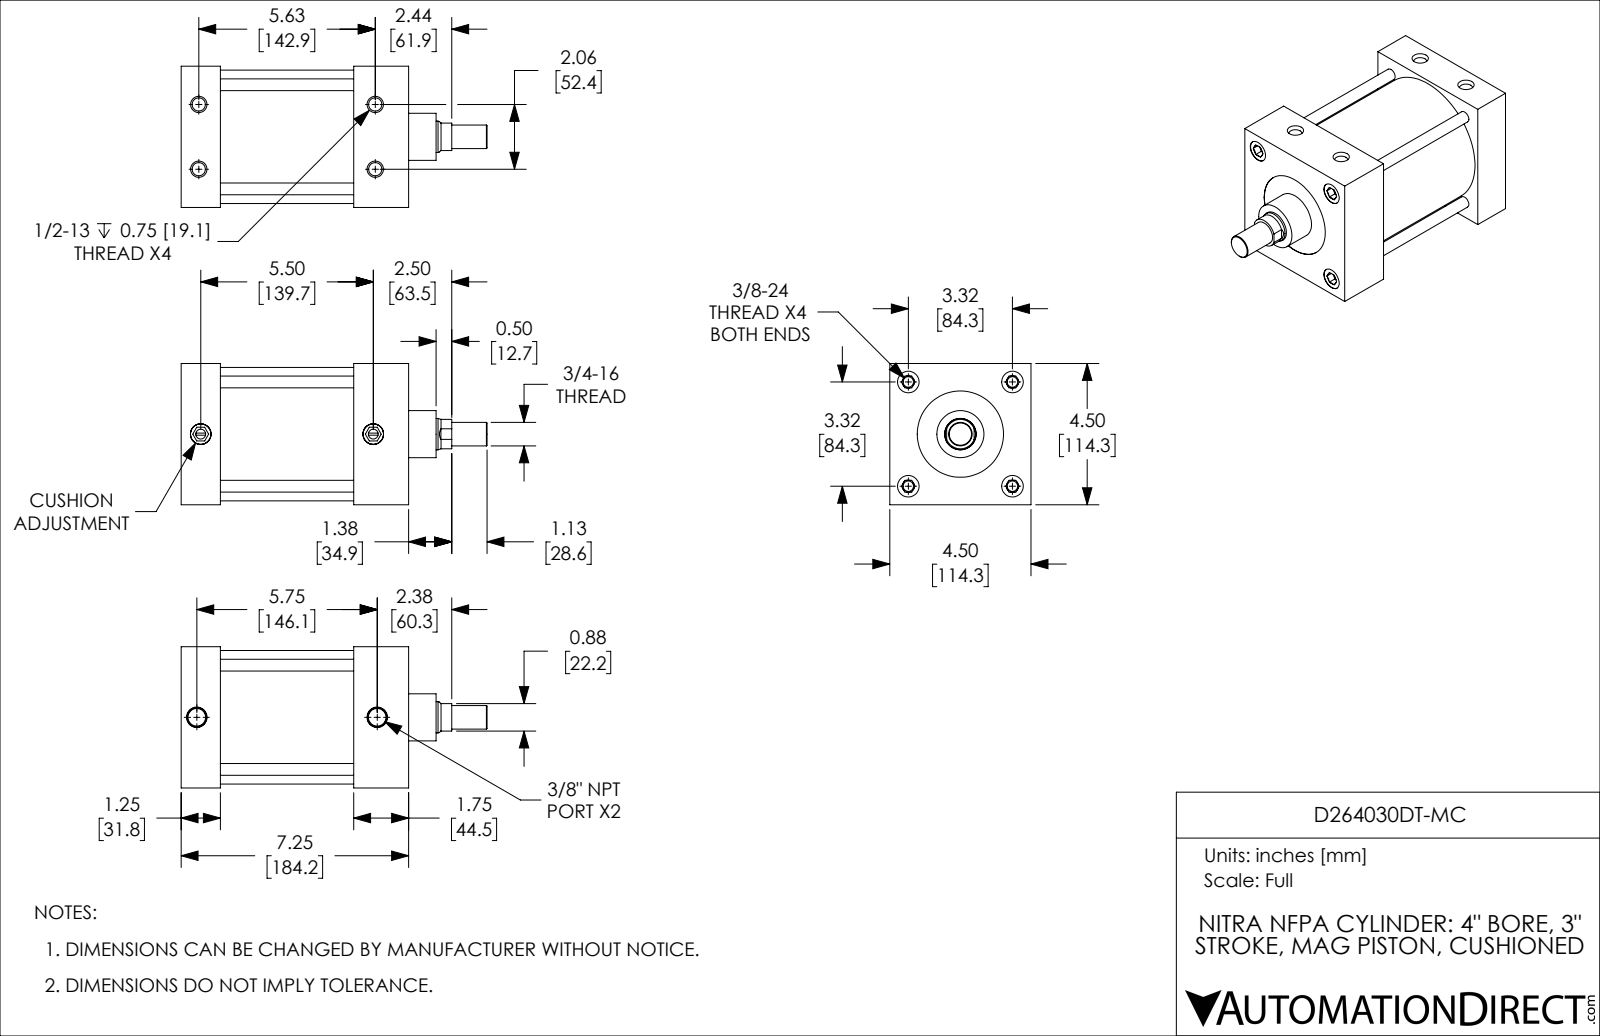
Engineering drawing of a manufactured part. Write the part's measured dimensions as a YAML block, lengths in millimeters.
part_name: "D264030DT-MC_CUSHION; D264030DT-MC_BODY; D264030DT-MC; D264030DT-MC_PISTON_KK1"
step_written_by: "SolidWorks 2019 (CONFIG_CONTROL_DESIGN)"
units: millimeters
bodies: {solids: 4, faces: 246, planar: 90, cylindrical: 78, other: 78}
overall_size: [247.7, 114.3, 114.3]
volume: 1434000
surface_area: 231000
round_holes:
  - {diameter: 8.4, count: 4}
  - {diameter: 10.7, count: 4}
  - {diameter: 17.4, count: 4}
  - {diameter: 7.9, count: 2}
  - {diameter: 14.3, count: 2}
  - {diameter: 16.7, count: 2}
  - {diameter: 25.4, count: 1}
  - {diameter: 69.9, count: 1}
  - {diameter: 101.6, count: 1}
round_bosses_or_shafts:
  - {diameter: 9.5, count: 4}
  - {diameter: 16.7, count: 2}
  - {diameter: 108, count: 1}
  - {diameter: 101.6, count: 1}
  - {diameter: 38.1, count: 1}
  - {diameter: 25.4, count: 1}
  - {diameter: 19.1, count: 1}
partial_cylinders:
  - {radius: 11.9, count: 1}
face_to_face_distances: [31.8, 114.3, 108, 139.7, 184.2, 152.4, 44.5, 63.5, 76.2, 120.7]
hole_center_spacings: [26.2, 59.6, 84.3, 146.8, 52.4, 119.3, 142.9, 152.2]
